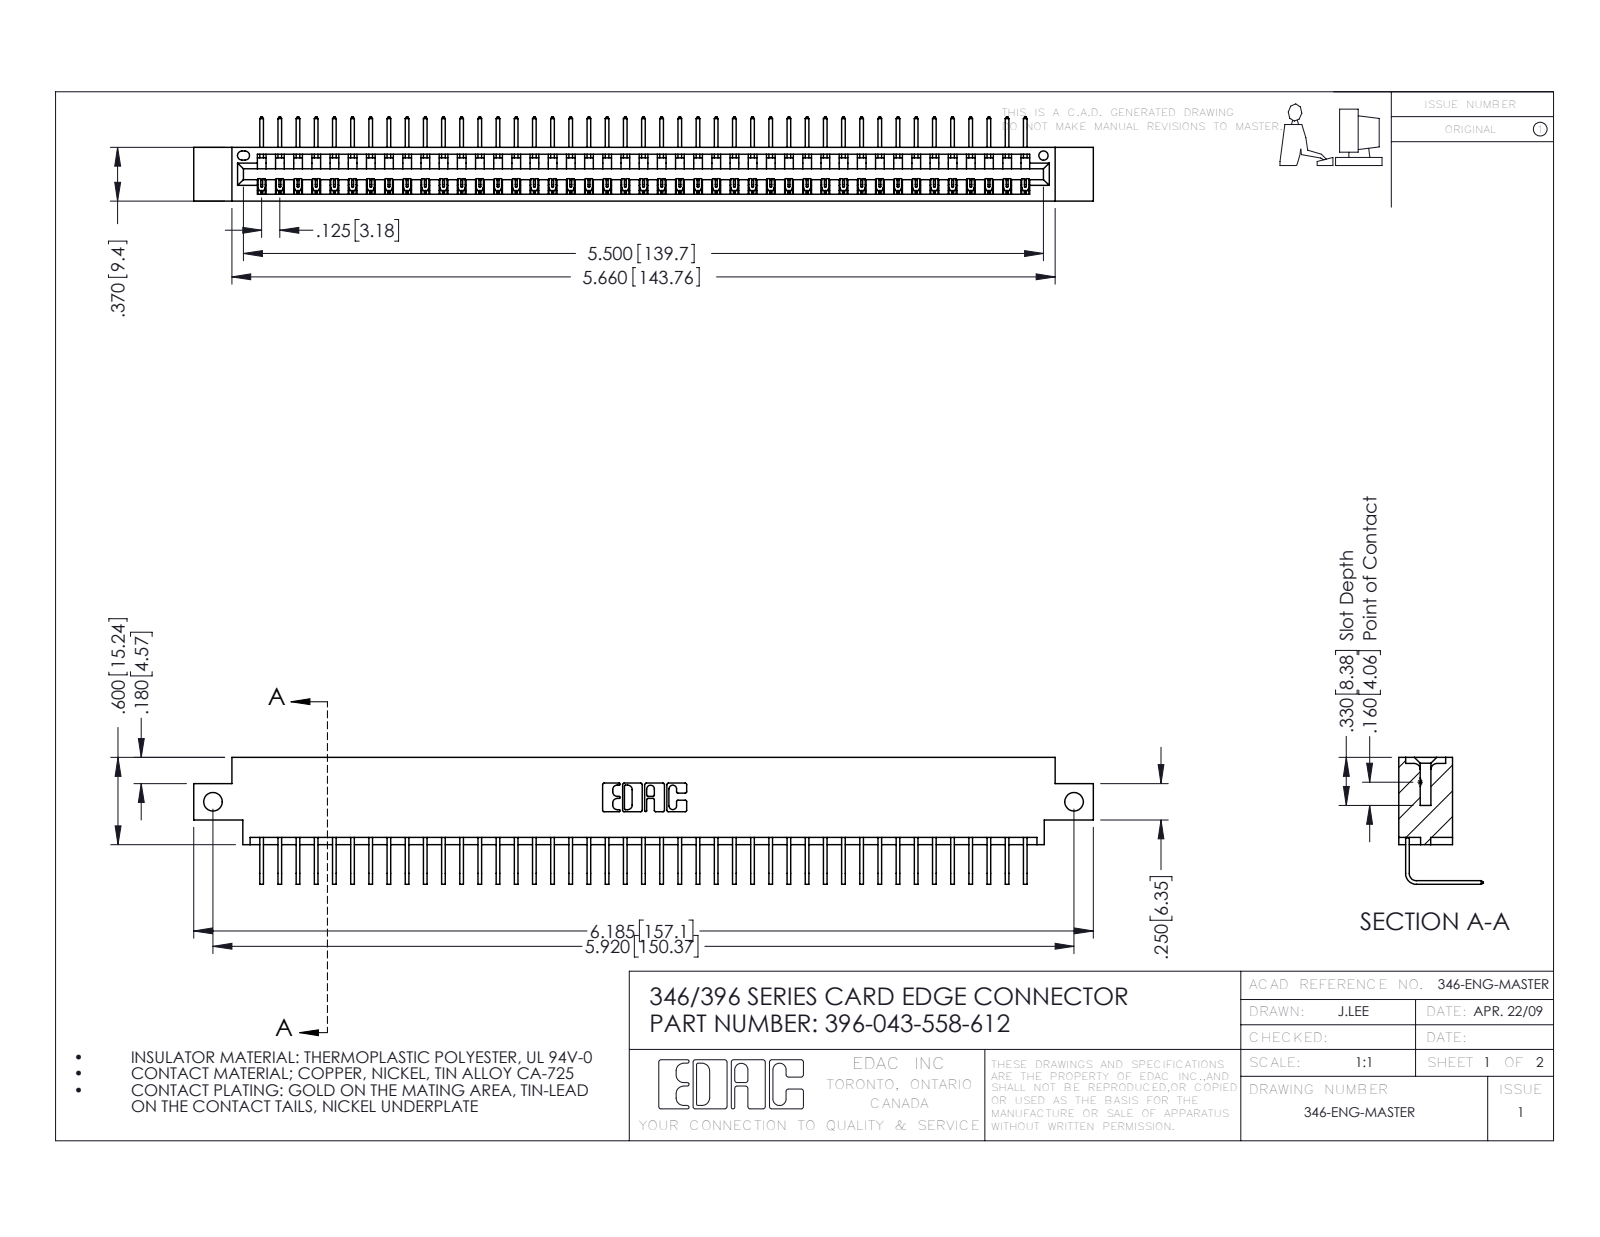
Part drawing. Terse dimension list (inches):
name: 345-292-001_558 Tail - 2; 346 Part_0.170 Offset - Side Mount; 396-043-558-612
written by: SolidWorks 2016 (CONFIG_CONTROL_DESIGN)
unit: in
bodies: 44 solids, 2706 faces (1886 planar, 820 cylindrical, 0 other)
size: 6.185 × 0.873 × 0.58
volume: 0.912 in³; area: 30.32 in²
holes: 2× ⌀0.128, 1× ⌀0.064
rounds: 86× R0.006, 22× R0.01, 6× R0.007, 6× R0.031, 3× R0.026, 2× R0.031, 2× R0.04, 1× R0.014
face distances: 0.322, 0.048, 0.37, 0.25, 0.298, 0.025, 0.072, 0.148, 0.222, 0.1
hole spacings: 5.92
